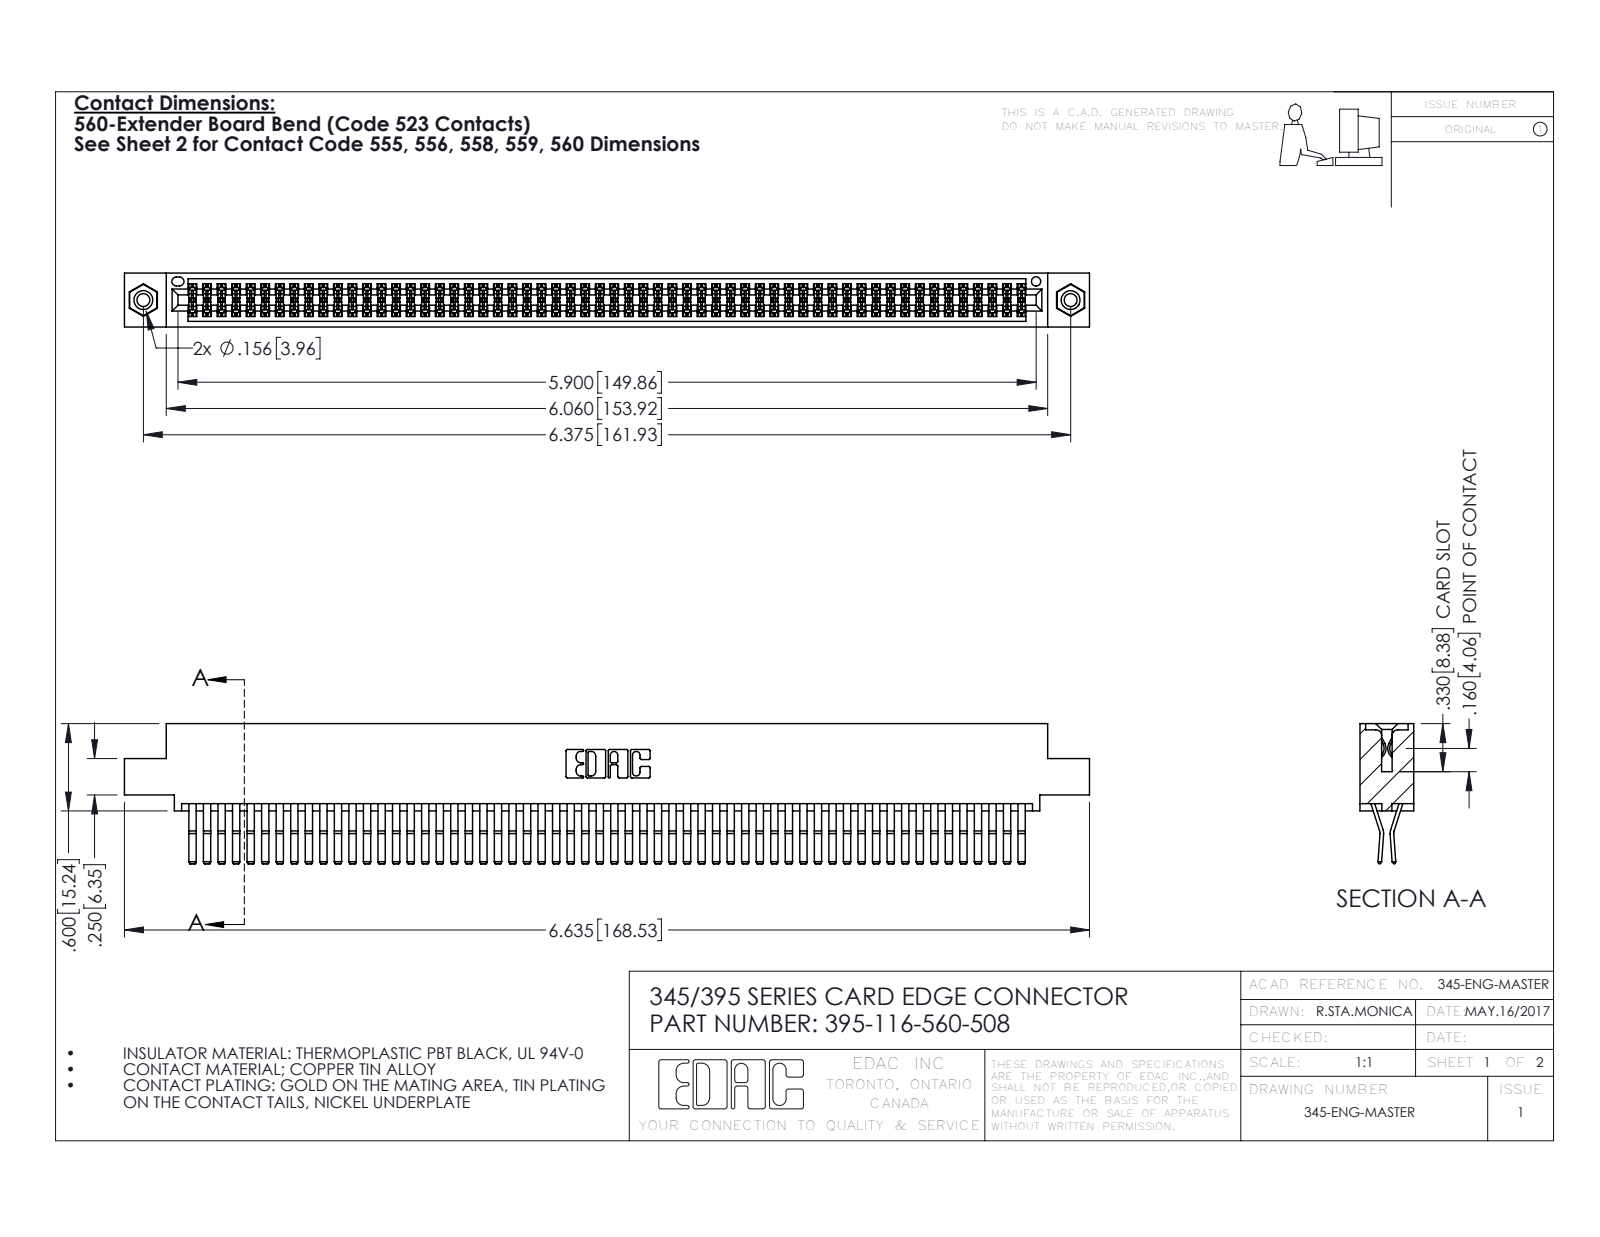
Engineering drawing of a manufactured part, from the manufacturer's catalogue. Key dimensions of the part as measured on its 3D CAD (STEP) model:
Part name (STEP PRODUCT): 395-116-560-508; 345-292-001_560 Tail; 345 Part_0.110 Offset - 0.156 Dia-TI; 345-250-001_345-250-003-102
STEP written by: SolidWorks 2016 (CONFIG_CONTROL_DESIGN)
Units: inches
Bodies: 119 solids, 6222 faces (3944 planar, 2262 cylindrical, 16 other)
Overall size (bounding box): 6.635 × 0.962 × 0.37
Volume: 1.05 in³ · Surface area: 43.08 in²
Round holes (diameter × count): ⌀0.089 ×2, ⌀0.125 ×2, ⌀0.156 ×2, ⌀0.064 ×1
Round bosses / shafts (diameter × count): ⌀0.155 ×2
Partial cylindrical surfaces — rounded edges, fillets, slot ends (radius × count): R0.006 ×175, R0.01 ×22, R0.007 ×6, R0.031 ×6, R0.026 ×3, R0.01 ×2, R0.014 ×2, R0.019 ×2
Main face-to-face distances: 0.025, 0.072, 0.298, 0.37, 0.2, 0.098, 0.272, 0.225, 0.175, 0.149
Hole centre spacings: 0.27, 6.139, 6.375
